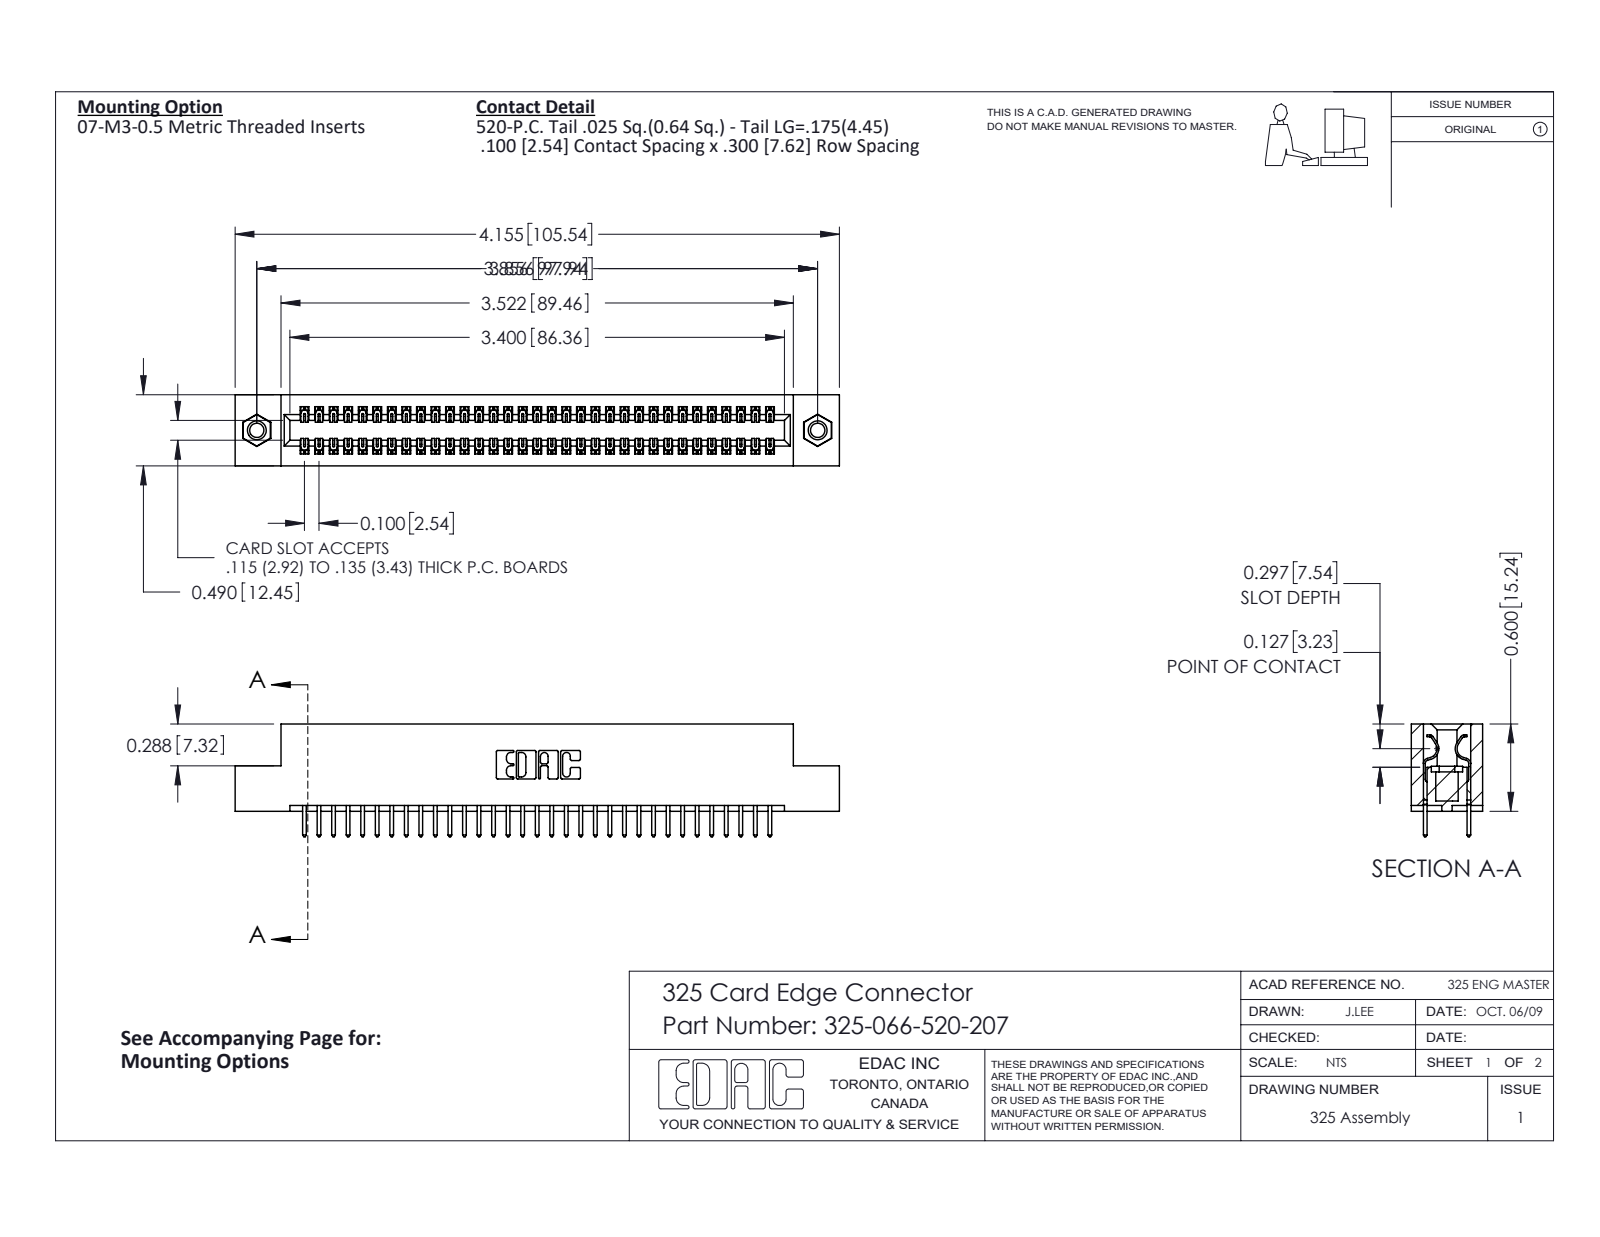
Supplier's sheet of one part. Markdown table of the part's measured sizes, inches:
| quantity | value |
| --- | --- |
| part name | 345-250-001_345-250-005-103; 325 Part_TI; 325-292-001_325-293-120; 325-066-520-207 |
| STEP written by | SolidWorks 2016 (CONFIG_CONTROL_DESIGN) |
| units | inches |
| bodies | 69 solids, 3606 faces (2478 planar, 1112 cylindrical, 16 other) |
| overall size | 4.155 × 0.775 × 0.49 |
| volume | 0.825 in³ |
| surface area | 24.87 in² |
| round holes (diameter × count) | 0.098 × 2, 0.125 × 2, 0.16 × 2 |
| round bosses / shafts (diameter × count) | 0.155 × 2 |
| partial cylindrical surfaces (radius × count) | 0.006 × 99, 0.01 × 66, 0.01 × 22, 0.007 × 6, 0.031 × 6, 0.026 × 3, 0.014 × 2, 0.022 × 2 |
| main face-to-face distances | 0.083, 0.407, 0.49, 0.3, 0.107, 0.383, 0.025, 0.325, 0.275, 0.56 |
| hole center spacings | 3.856 |
